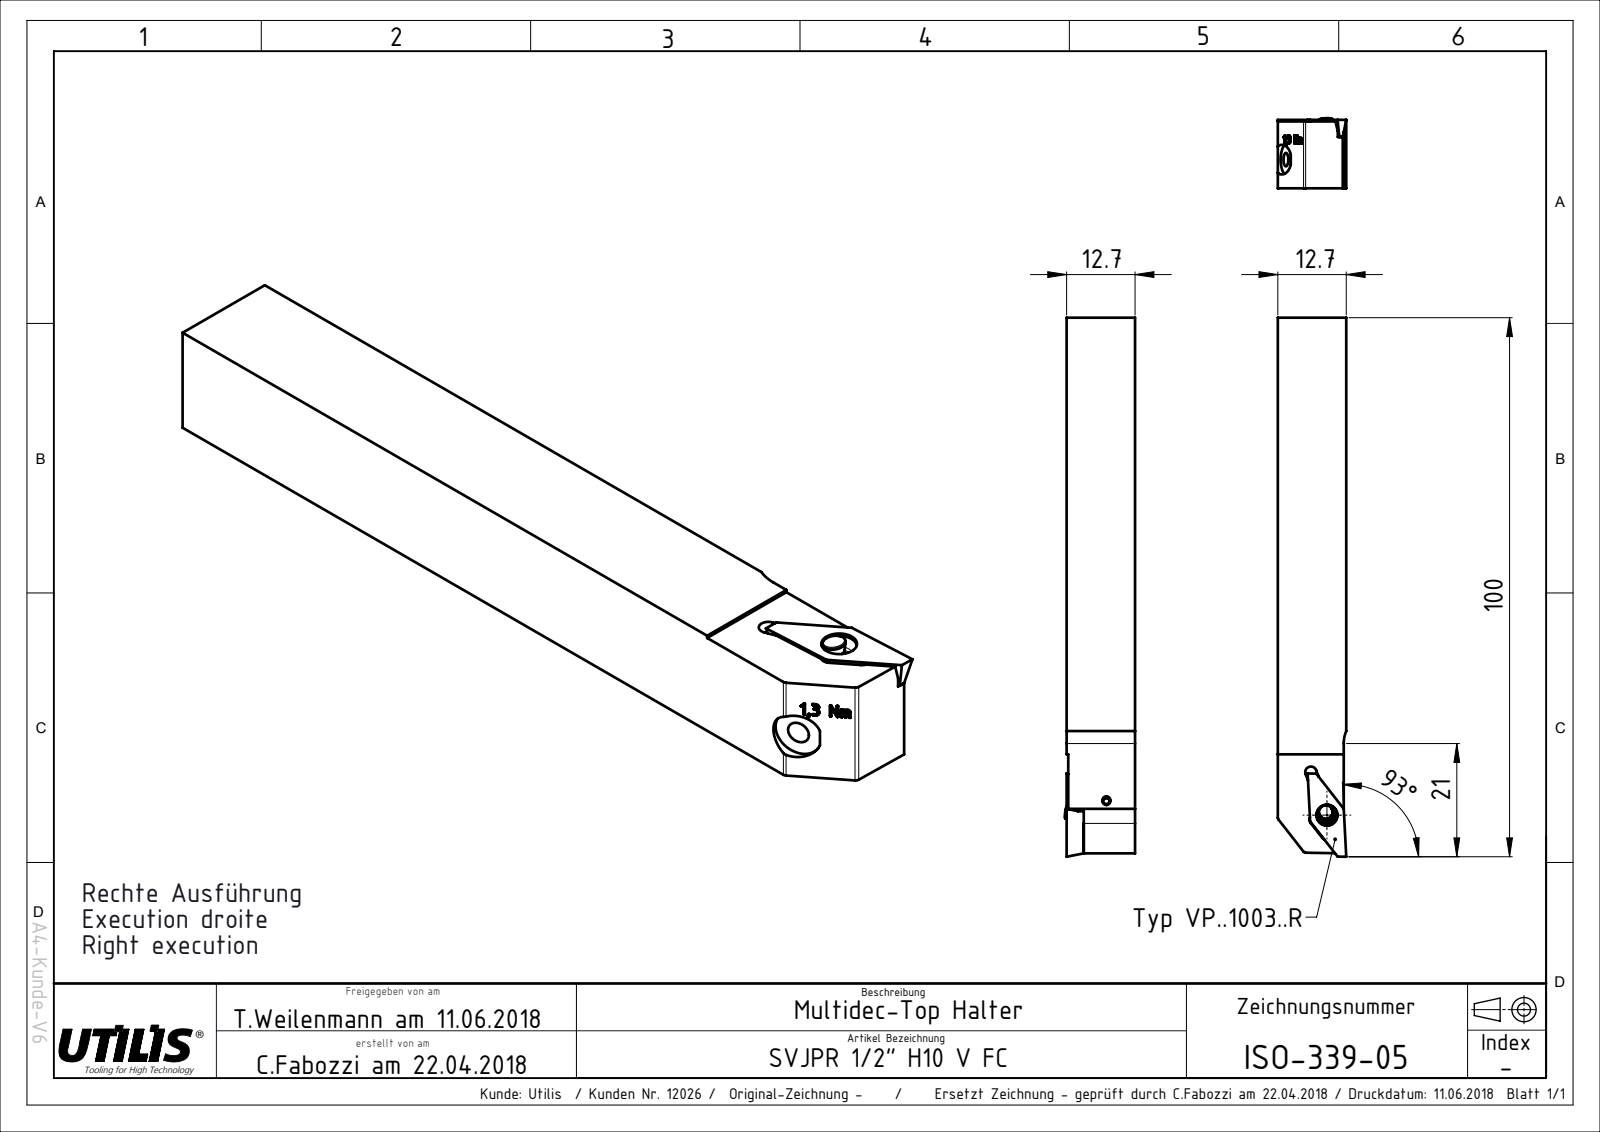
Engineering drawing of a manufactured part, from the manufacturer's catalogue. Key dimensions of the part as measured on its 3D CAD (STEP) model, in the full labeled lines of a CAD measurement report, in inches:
Part name (STEP PRODUCT): ISO-339-05
STEP written by: SolidWorks 2018 (AUTOMOTIVE_DESIGN)
Units: inches
Bodies: 1 solid, 110 faces (58 planar, 8 cylindrical, 44 other)
Overall size (bounding box): 3.937 × 0.5 × 0.5
Volume: 0.952 in³ · Surface area: 8.345 in²
Partial cylindrical surfaces — rounded edges, fillets, slot ends (radius × count): R0.041 ×3, R0.02 ×2, R0.236 ×1, R0.24 ×1
Main face-to-face distances: 0.5, 0.481, 0.019, 0.488, 0.125, 0.113, 0.375, 0.17, 0.408, 0.238
